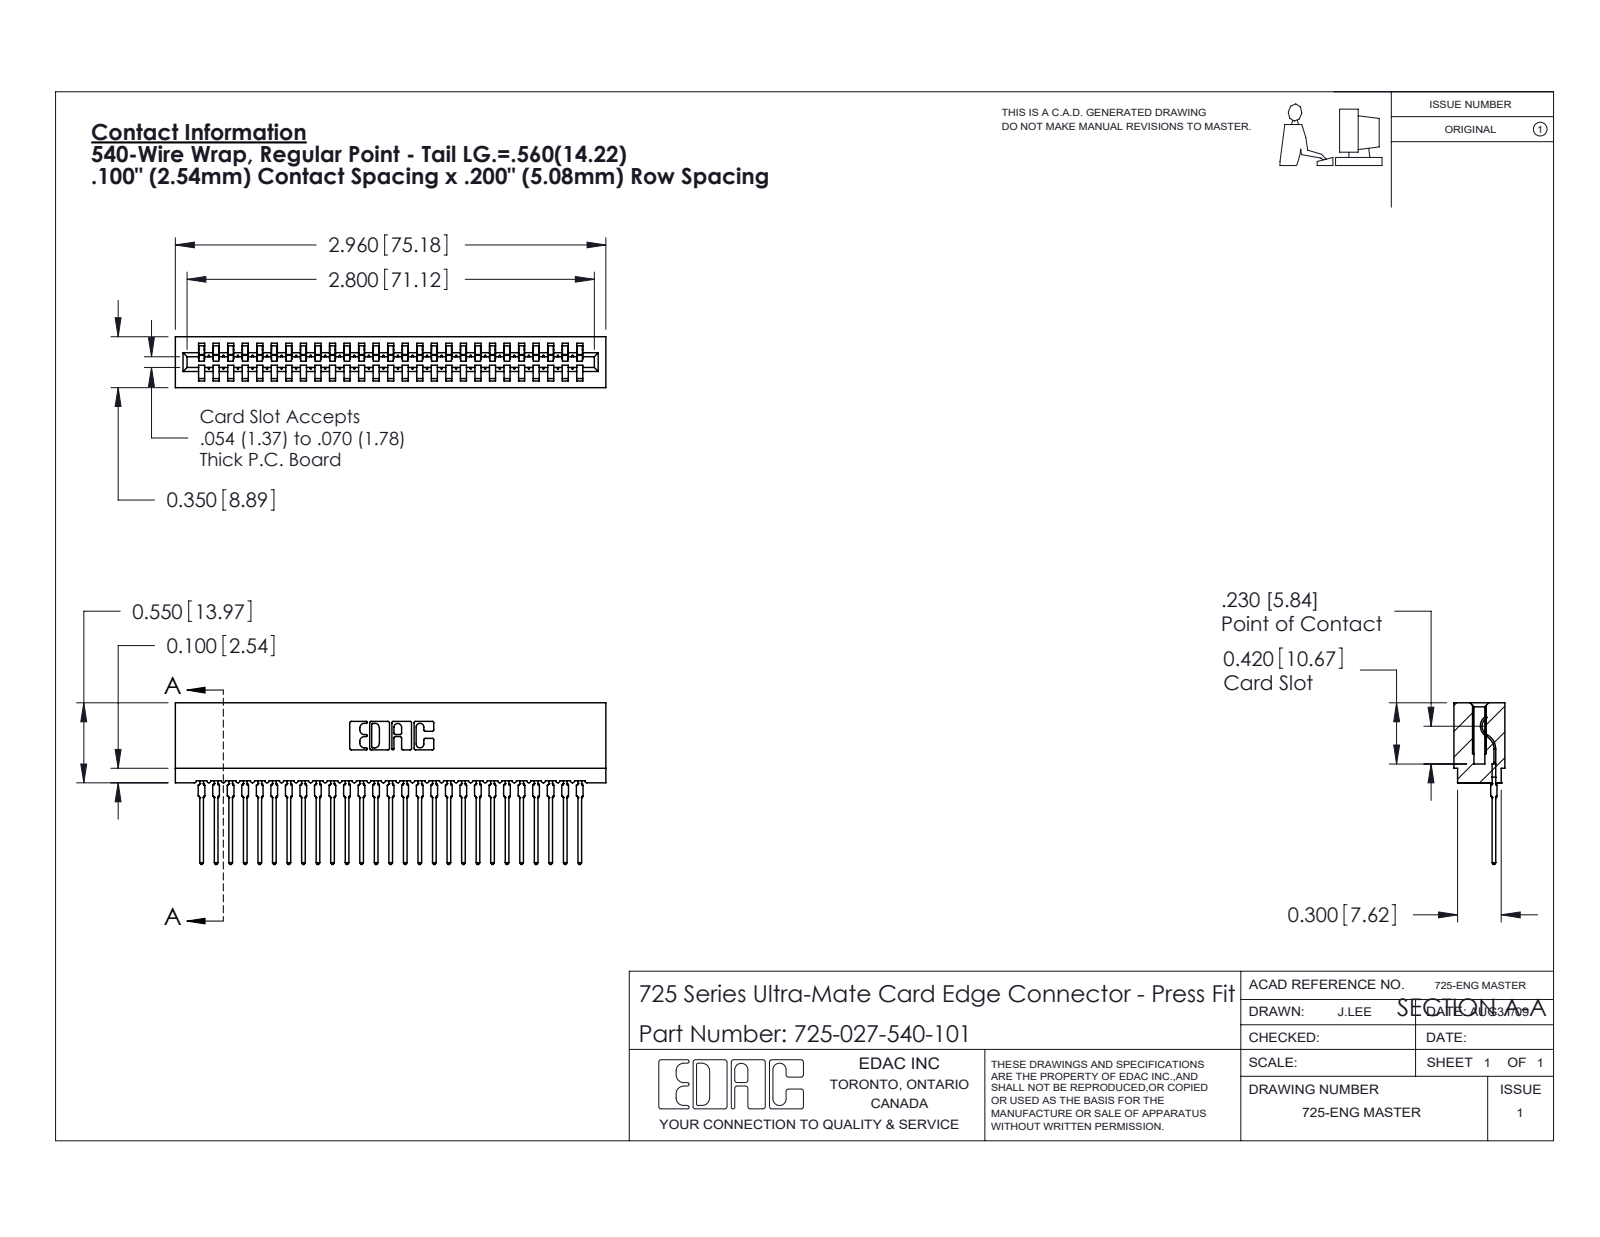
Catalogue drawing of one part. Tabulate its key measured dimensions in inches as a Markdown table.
| quantity | value |
| --- | --- |
| part name | 745-292-001_540; 725-027-540-101; 725 Part_Insulator Option - 01 |
| STEP written by | SolidWorks 2020 (CONFIG_CONTROL_DESIGN) |
| units | inches |
| bodies | 28 solids, 3119 faces (1864 planar, 553 cylindrical, 702 other) |
| overall size | 2.96 × 1.111 × 0.35 |
| volume | 0.357 in³ |
| surface area | 17.5 in² |
| partial cylindrical surfaces (radius × count) | 0.015 × 54, 0.021 × 54, 0.01 × 22, 0.007 × 6, 0.031 × 6, 0.005 × 4, 0.011 × 4, 0.026 × 3 |
| main face-to-face distances | 0.1, 0.35, 0.2, 0.3, 0.6, 0.212, 0.138, 0.063, 0.287, 0.4 |
